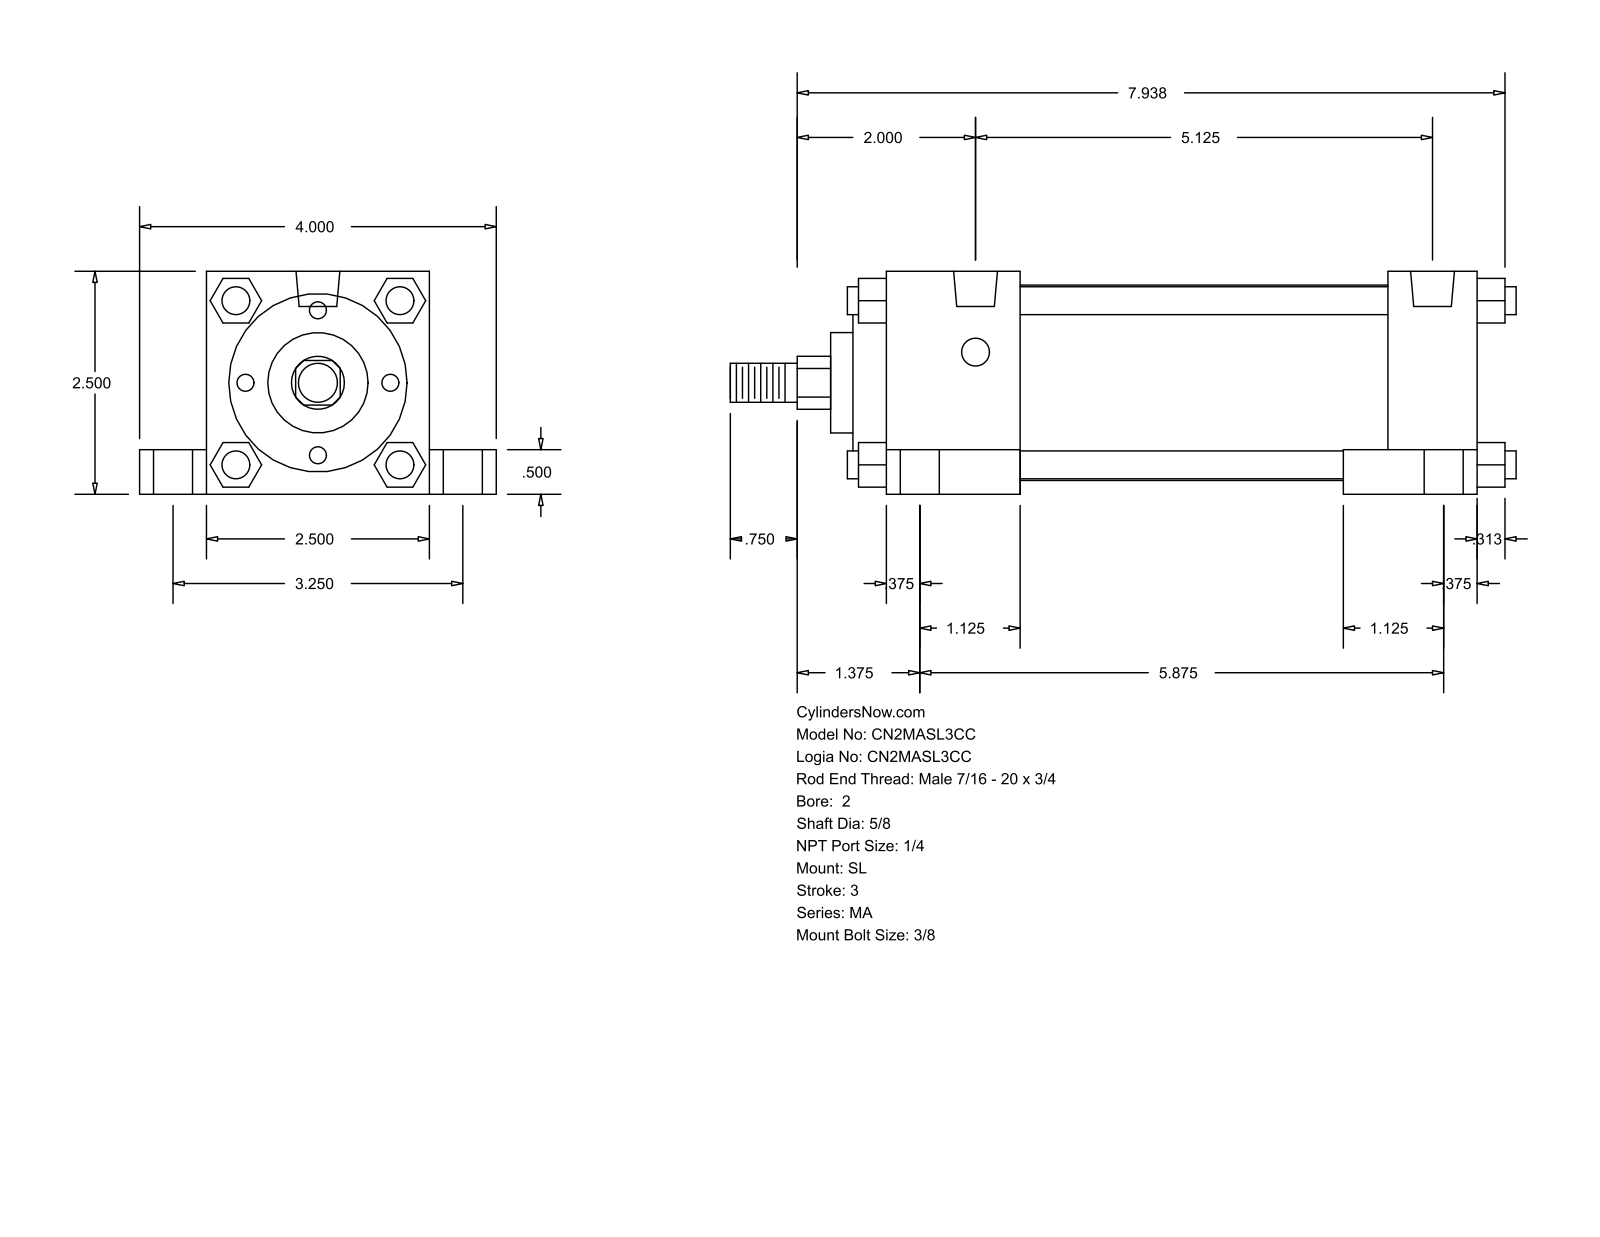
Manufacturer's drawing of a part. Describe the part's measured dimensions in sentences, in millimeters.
The part is named "MA_SL__0200_0.625". Its 3-D file was written by "GSSL Pune (CONFIG_CONTROL_DESIGN)". It is 0 solids with 150 faces: 113 planar, 37 cylindrical and 0 other. Overall it measures 223.84 by 101.6 by 63.5 millimeters. Round holes: 4 of diameter 7.94, 4 of diameter 11.11, 4 of diameter 17.46, 2 of diameter 12.49. Round bosses or shafts: 4 of diameter 7.94, 1 of diameter 55.63, 1 of diameter 50.8, 1 of diameter 28.57, 1 of diameter 15.88, 1 of diameter 11.11. Partial cylindrical surfaces (rounded edges, fillets, slot ends): 1 of radius 7.54. The main face-to-face distances are 63.5, 12.7, 9.52, 25.4, 19.05, 82.55, 38.1, 168.28, 50.8, 130.18. The hole center spacings are 41.39, 44.22, 82.54, 130.17, 139.59, 149.23, 151.77, 170.54.
